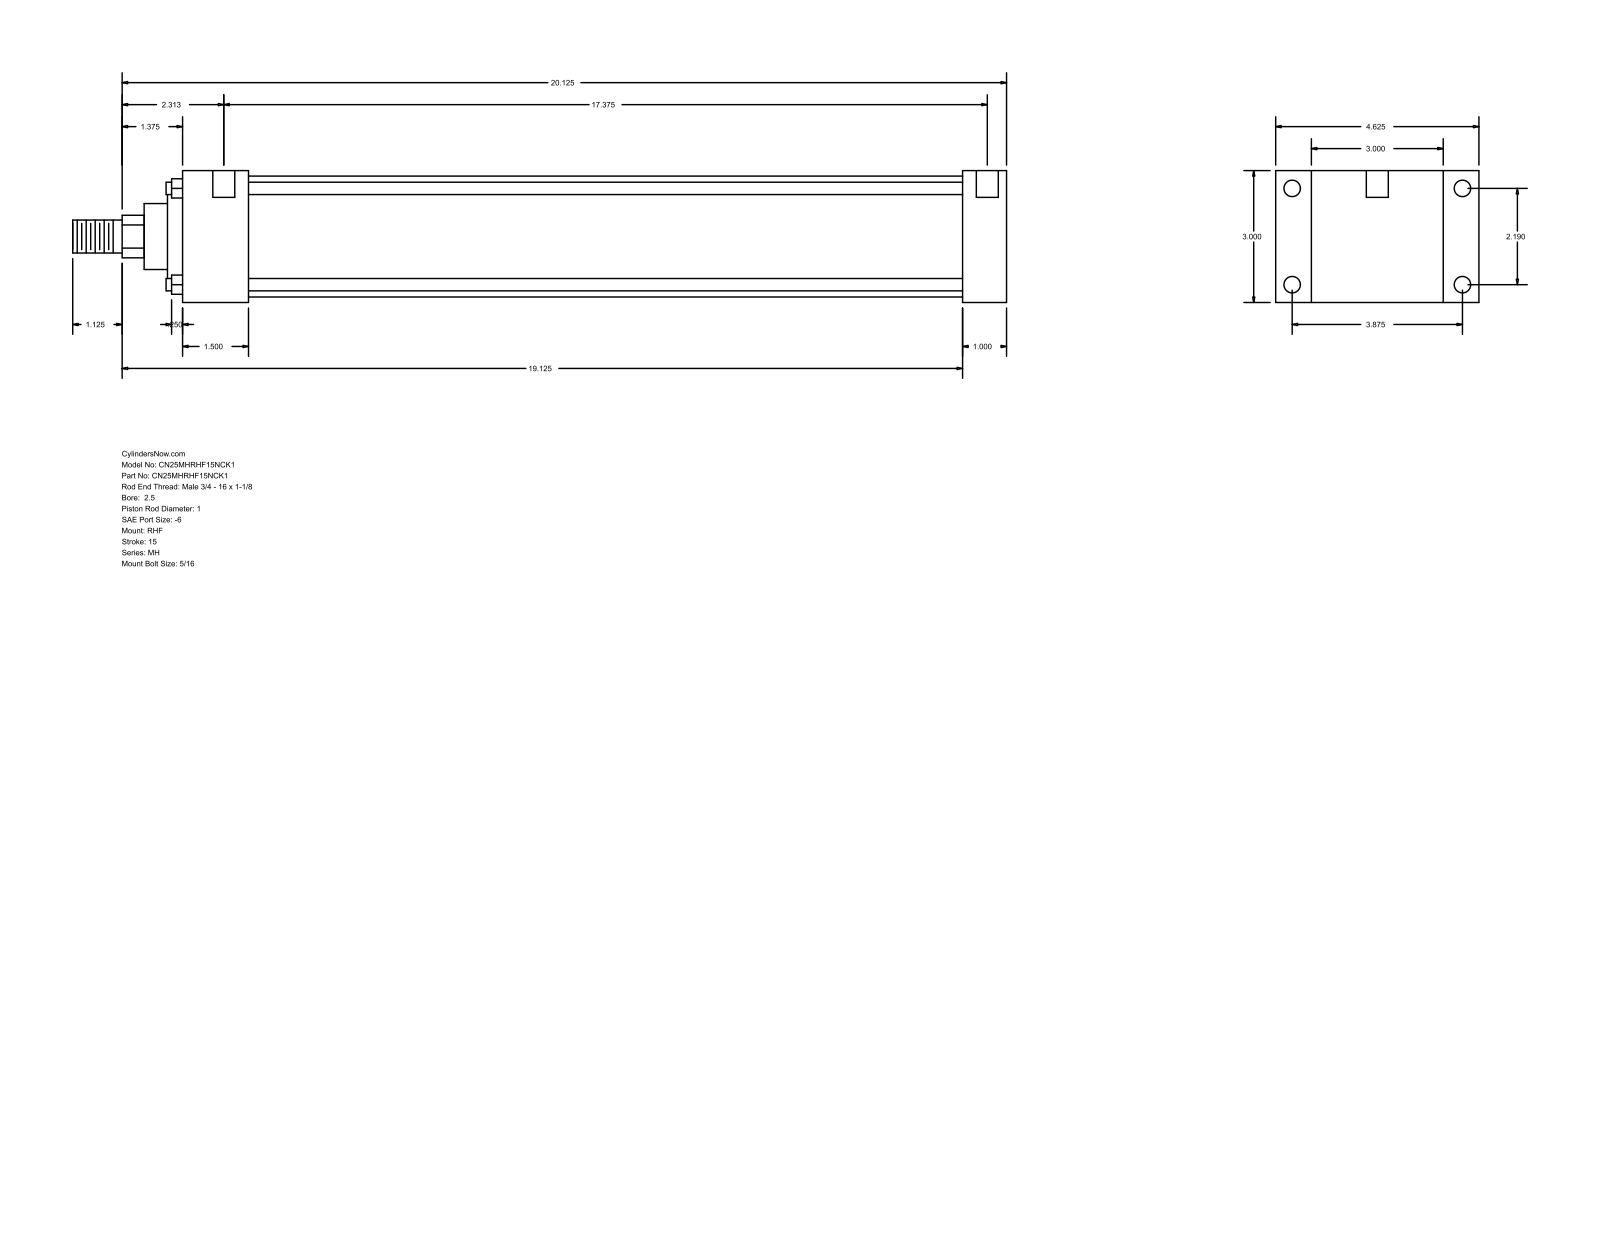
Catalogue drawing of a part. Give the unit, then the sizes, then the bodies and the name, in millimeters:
Units: millimetres
Overall size (bounding box): 539.75 × 117.47 × 76.2
Round holes (diameter × count): ⌀5.56 ×4, ⌀9.53 ×4, ⌀12.7 ×2
Round bosses / shafts (diameter × count): ⌀7.14 ×4, ⌀69.85 ×1, ⌀60.33 ×1, ⌀38.1 ×1, ⌀25.4 ×1, ⌀19.05 ×1
Partial cylindrical surfaces — rounded edges, fillets, slot ends (radius × count): R12.29 ×1
Main face-to-face distances: 76.2, 25.41, 20.64, 96.84, 450.85, 476.26, 117.48, 38.11, 412.74, 438.15
Hole centre spacings: 55.62, 98.42, 113.05, 449.26, 3.18, 4.76, 441.32, 444.5
Bodies: 0 solids, 90 faces (61 planar, 29 cylindrical, 0 other)
Part name (STEP PRODUCT): MH_RHF__0250_1
STEP written by: GSSL Pune (CONFIG_CONTROL_DESIGN)
